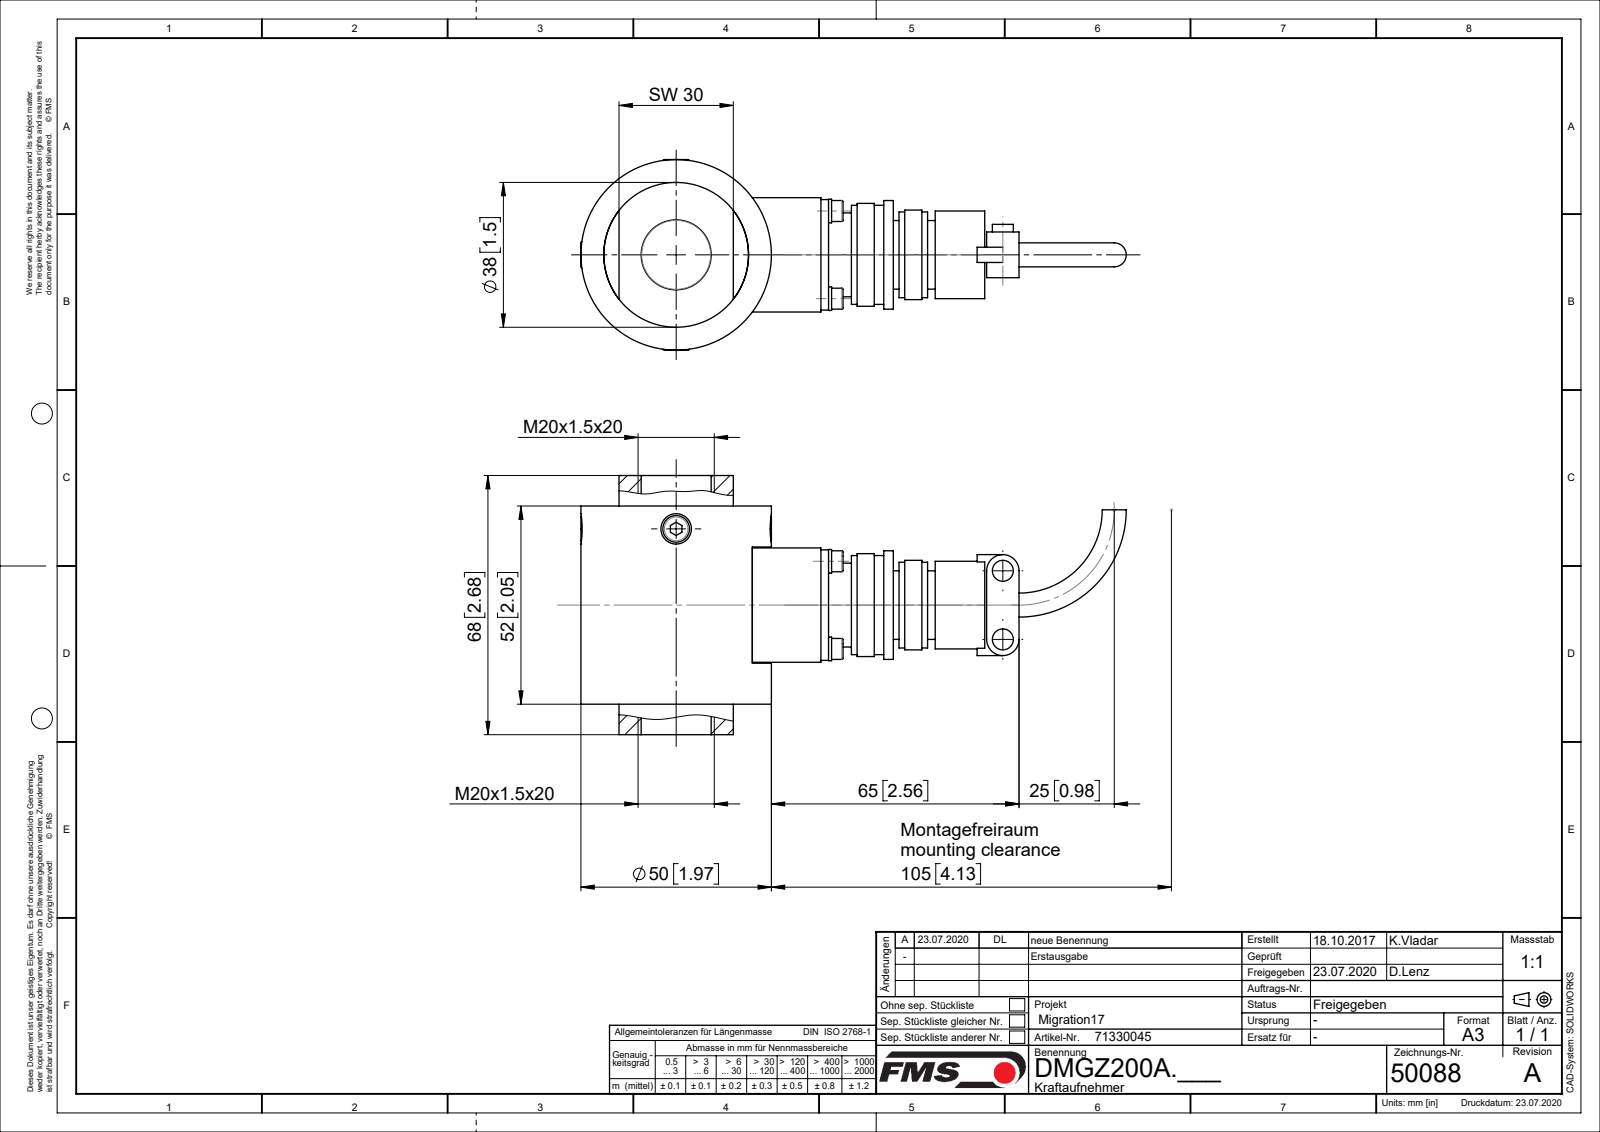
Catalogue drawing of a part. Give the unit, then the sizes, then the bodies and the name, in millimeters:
Units: millimetres
Overall size (bounding box): 143.15 × 68 × 50
Round holes (diameter × count): ⌀3.42 ×6, ⌀3.2 ×4, ⌀3.4 ×4, ⌀4.3 ×2, ⌀8 ×2, ⌀18.68 ×1, ⌀20.5 ×1, ⌀23 ×1, ⌀38 ×1
Round bosses / shafts (diameter × count): ⌀5.5 ×6, ⌀6.2 ×4, ⌀3 ×4, ⌀2.5 ×4, ⌀7 ×2, ⌀4 ×2, ⌀50 ×1, ⌀28.5 ×1
Partial cylindrical surfaces — rounded edges, fillets, slot ends (radius × count): R4.25 ×2
Main face-to-face distances: 30, 8, 19, 60, 41, 18, 11, 49, 42, 52
Hole centre spacings: 16.26, 23, 14.3, 32.53, 33.53, 20
Volume: 137 846 mm³ · Surface area: 45 508 mm²
Bodies: 16 solids, 298 faces (96 planar, 156 cylindrical, 46 other)
Part name (STEP PRODUCT): D50088; L49026; TEIL1; I-6KT_SCHRAUBE_M4X10 (+6 more)
STEP written by: Mechanical Desktop 2007 (CONFIG_CONTROL_DESIGN)
